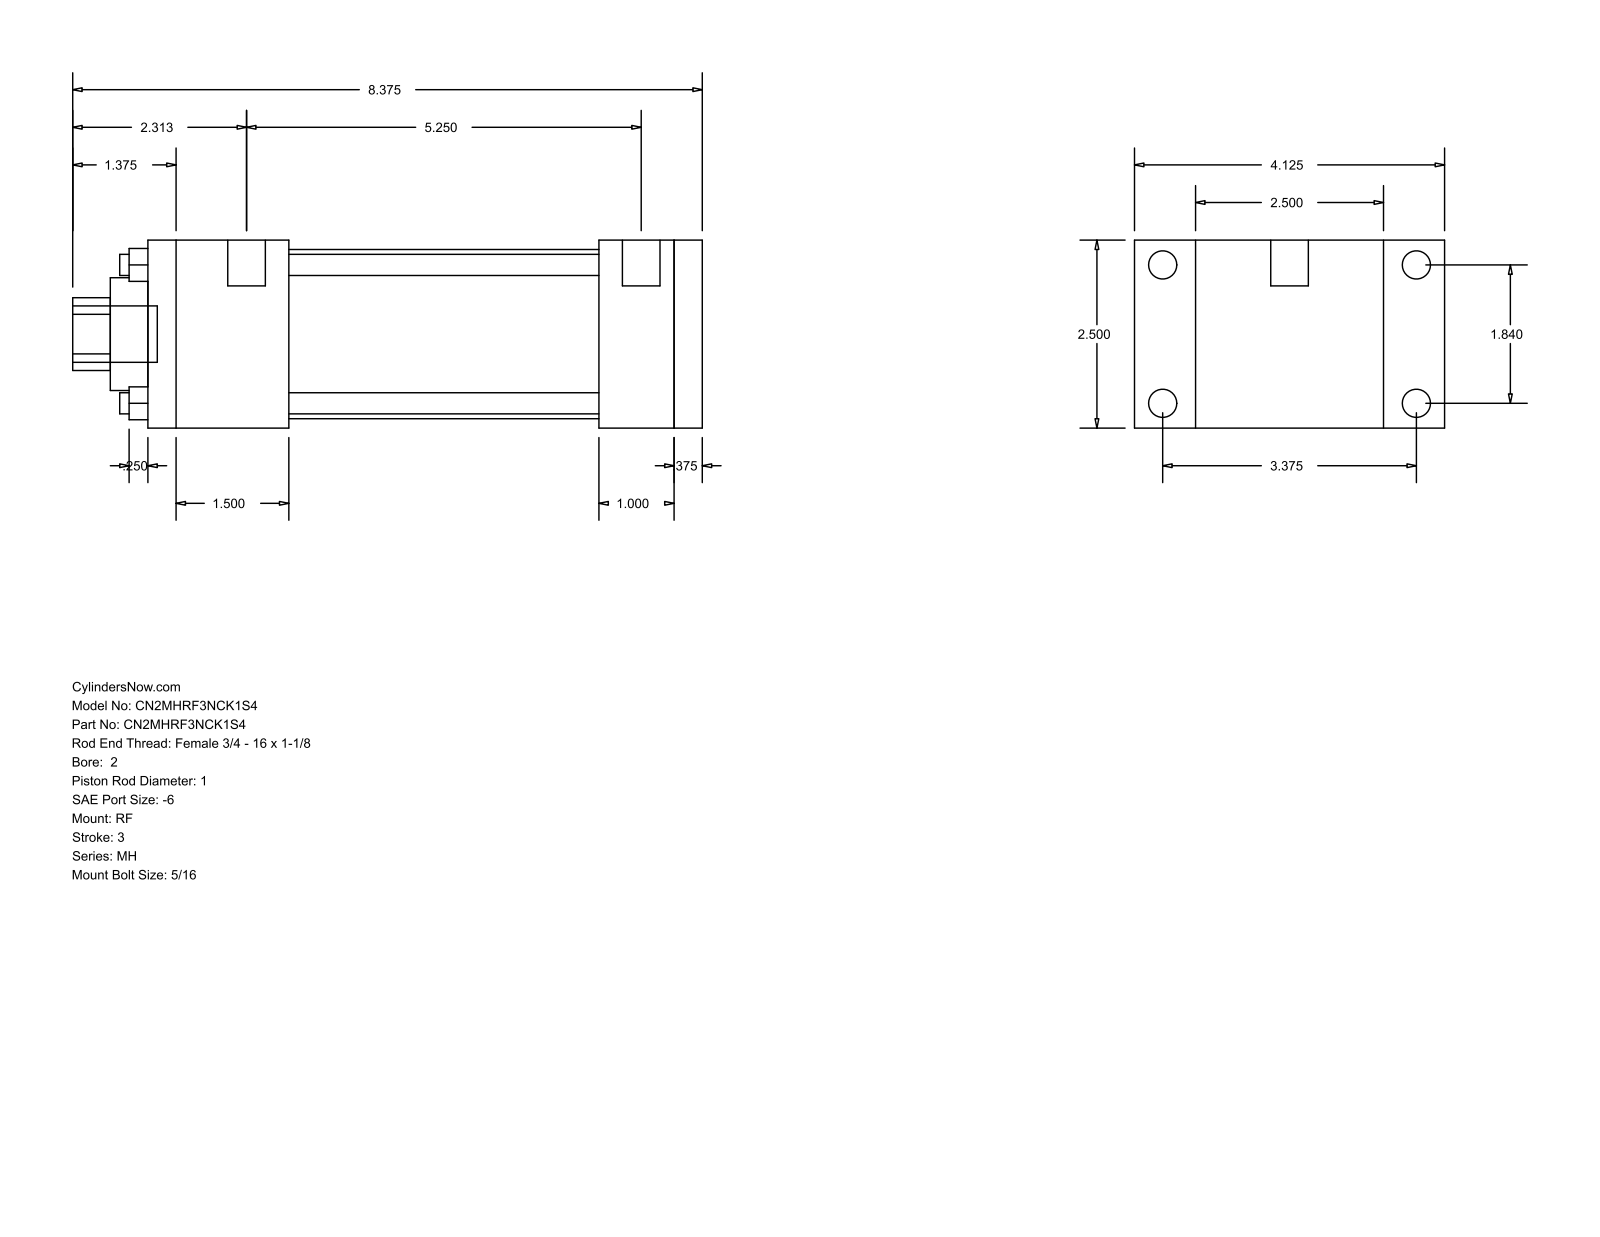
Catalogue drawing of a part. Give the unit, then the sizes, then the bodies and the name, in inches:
Units: inches
Overall size (bounding box): 8.375 × 4.125 × 2.5
Round holes (diameter × count): ⌀0.281 ×4, ⌀1 ×1, ⌀1.5 ×1, ⌀2.25 ×1
Round bosses / shafts (diameter × count): ⌀0.375 ×4, ⌀0.219 ×4, ⌀0.5 ×2, ⌀0.75 ×1
Partial cylindrical surfaces — rounded edges, fillets, slot ends (radius × count): R0.484 ×1
Main face-to-face distances: 2.5, 0.375, 7.375, 7, 0.813, 1, 1.875, 6, 4.125, 5.125
Hole centre spacings: 1.301, 1.84, 2.602
Bodies: 0 solids, 92 faces (64 planar, 28 cylindrical, 0 other)
Part name (STEP PRODUCT): MH_RF__0200_1
STEP written by: GSSL Pune (CONFIG_CONTROL_DESIGN)
